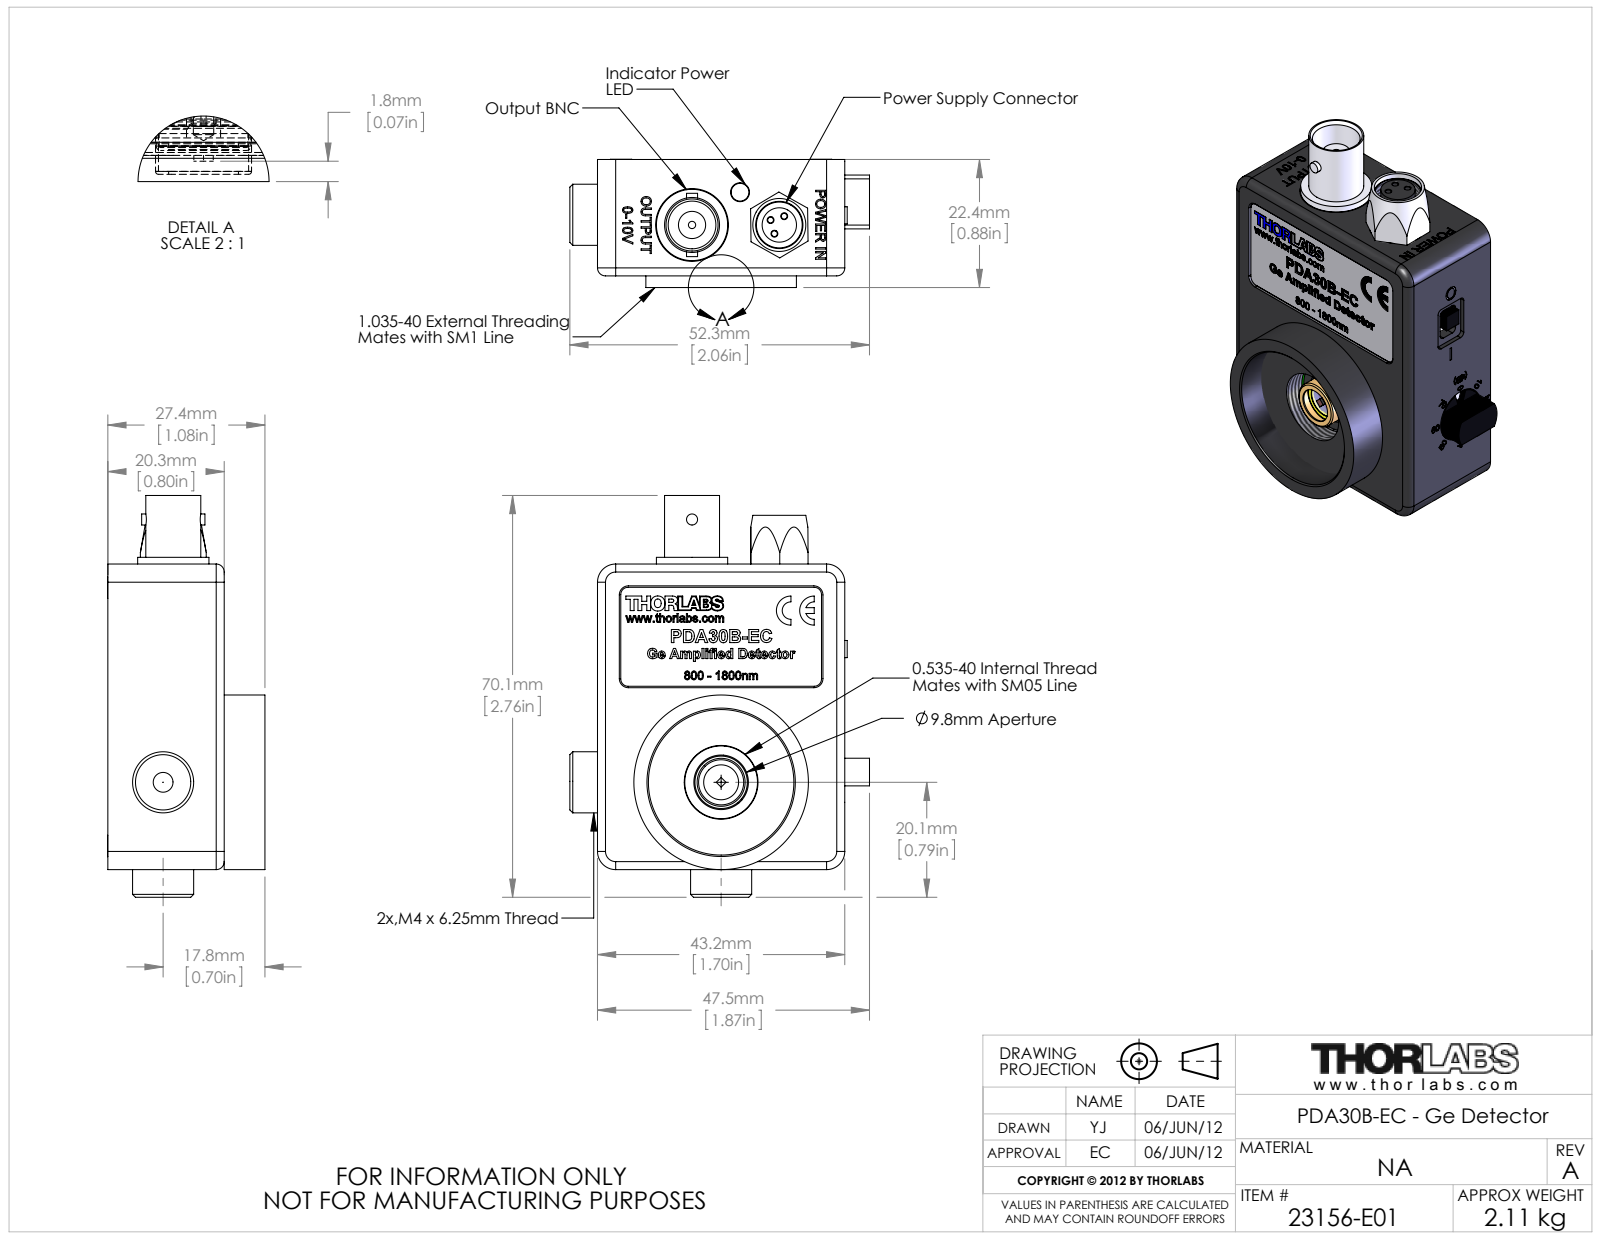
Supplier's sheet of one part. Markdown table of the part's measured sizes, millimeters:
| quantity | value |
| --- | --- |
| part name | 13053-001_Etching; pcb; 23155-002_PDA30B-EC-LB1; 23156-E0W (+8 more) |
| STEP written by | SolidWorks 2011 (AUTOMOTIVE_DESIGN) |
| units | millimeters |
| bodies | 25 solids, 2335 faces (1174 planar, 378 cylindrical, 783 other) |
| overall size | 70.1 × 52.3 × 27.5 |
| volume | 25 740 mm³ |
| surface area | 31 970 mm² |
| round holes (diameter × count) | 0.9 × 9, 0.8 × 8, 1.8 × 7, 2.4 × 7, 0.8 × 6, 3.2 × 4, 5.1 × 4, 0.7 × 3, 0.8 × 3, 1 × 3, 1.3 × 3, 1.7 × 2 |
| round bosses / shafts (diameter × count) | 2.2 × 7, 0.5 × 6, 3.7 × 4, 3.6 × 3, 0.4 × 3, 10.7 × 2, 9.4 × 2, 6 × 2 |
| partial cylindrical surfaces (radius × count) | 3.2 × 23, 0.8 × 14, 2.4 × 8, 0.1 × 4, 1.3 × 4, 1.4 × 4, 0.6 × 3, 1.6 × 3 |
| main face-to-face distances | 1.6, 12.8, 14.4, 2.5, 12.8, 11.2, 1.6, 1.3, 1.8, 4.2 |
| hole center spacings | 2.5, 3.6, 2.5, 5.1, 11, 11.1, 13.5, 13.6 |
